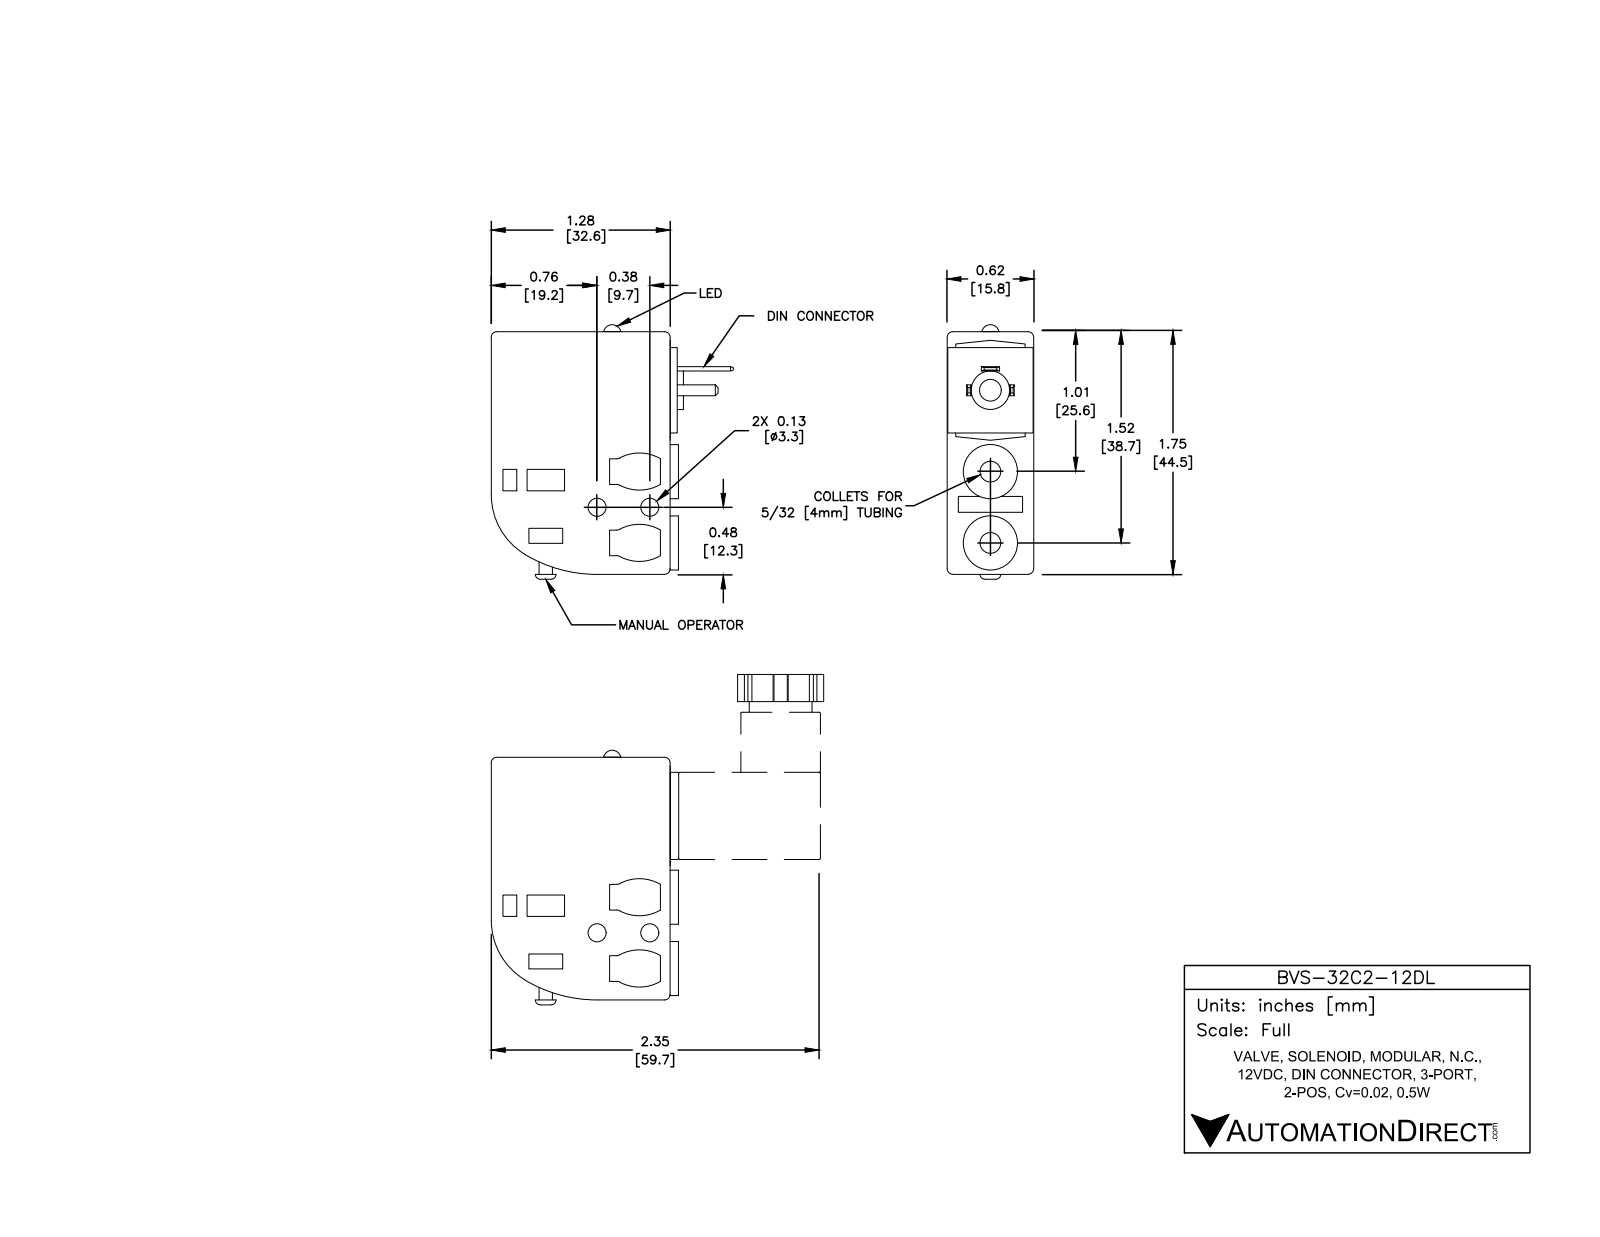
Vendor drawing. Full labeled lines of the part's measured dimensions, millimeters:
Part name (STEP PRODUCT): BVS-32C2-12DL
STEP written by: SolidWorks 2016 (AUTOMOTIVE_DESIGN)
Units: millimetres
Bodies: 1 solid, 162 faces (112 planar, 46 cylindrical, 4 other)
Overall size (bounding box): 46.7 × 44.5 × 15.7
Volume: 20 960 mm³ · Surface area: 6 935 mm²
Round holes (diameter × count): ⌀3.3 ×2, ⌀3.8 ×2, ⌀6.4 ×2, ⌀1.3 ×1, ⌀4.1 ×1
Round bosses / shafts (diameter × count): ⌀9.9 ×2, ⌀7.1 ×1, ⌀2.5 ×1
Partial cylindrical surfaces — rounded edges, fillets, slot ends (radius × count): R1.3 ×4, R7.6 ×4, R1 ×3, R12.7 ×1, R25.4 ×1
Main face-to-face distances: 15.7, 2.5, 32.8, 13.2, 34.1, 1.3, 44.5, 25.4, 3.8, 1.5
Hole centre spacings: 1.5, 9.7, 11.4, 13, 15, 16.5, 27.9
